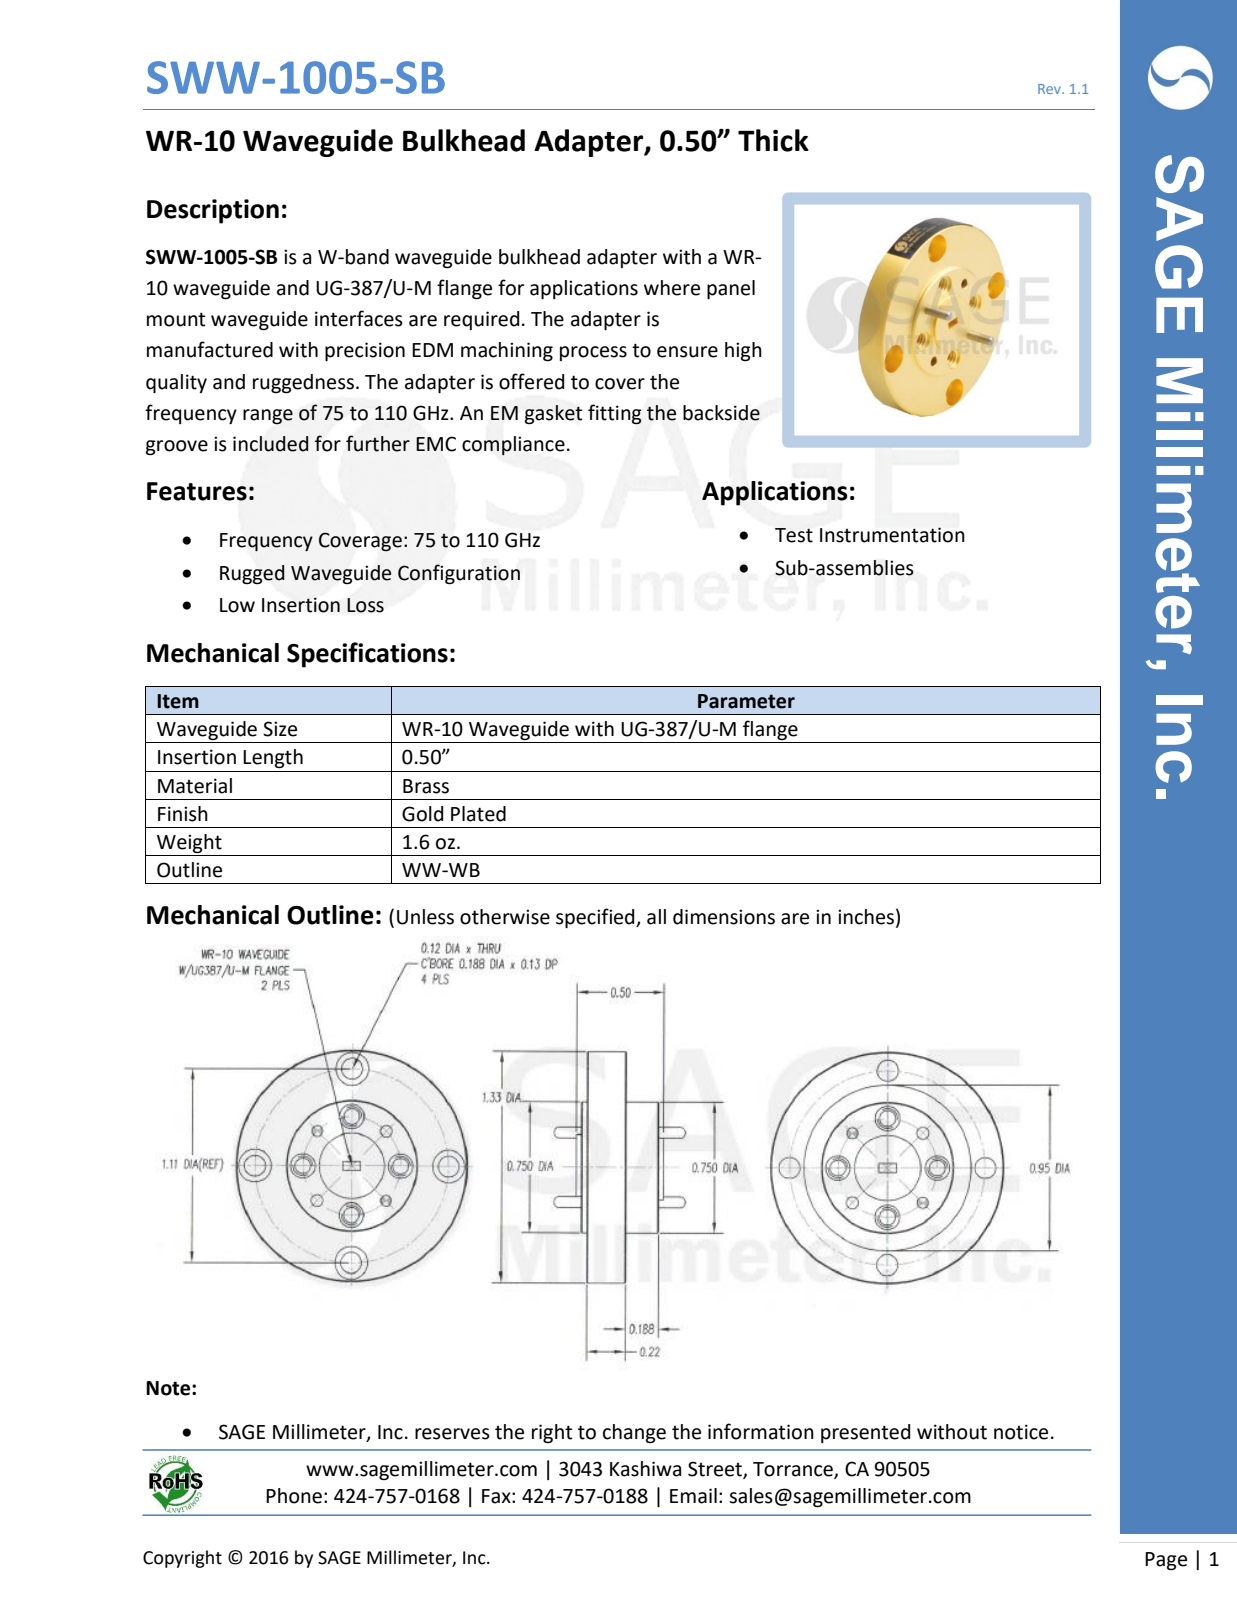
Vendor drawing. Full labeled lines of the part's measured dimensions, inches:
Part name (STEP PRODUCT): WW-WB-A, Defeatured
STEP written by: SolidWorks 2021 (AUTOMOTIVE_DESIGN)
Units: inches
Bodies: 1 solid, 175 faces (35 planar, 84 cylindrical, 56 other)
Overall size (bounding box): 1.325 × 1.325 × 0.758
Volume: 0.367 in³ · Surface area: 5.893 in²
Round holes (diameter × count): ⌀0.067 ×4, ⌀0.089 ×4, ⌀0.12 ×4, ⌀0.14 ×4, ⌀0.188 ×4, ⌀0.68 ×1, ⌀0.95 ×1
Round bosses / shafts (diameter × count): ⌀0.063 ×4, ⌀1.325 ×1, ⌀0.75 ×1, ⌀0.375 ×1
Main face-to-face distances: 0.222, 0.02, 0.48, 0.147, 0.075, 0.04, 0.42, 0.06, 0.44, 0.187
Hole centre spacings: 0.215, 0.281, 0.398, 0.408, 0.519, 0.622, 0.78, 0.274
